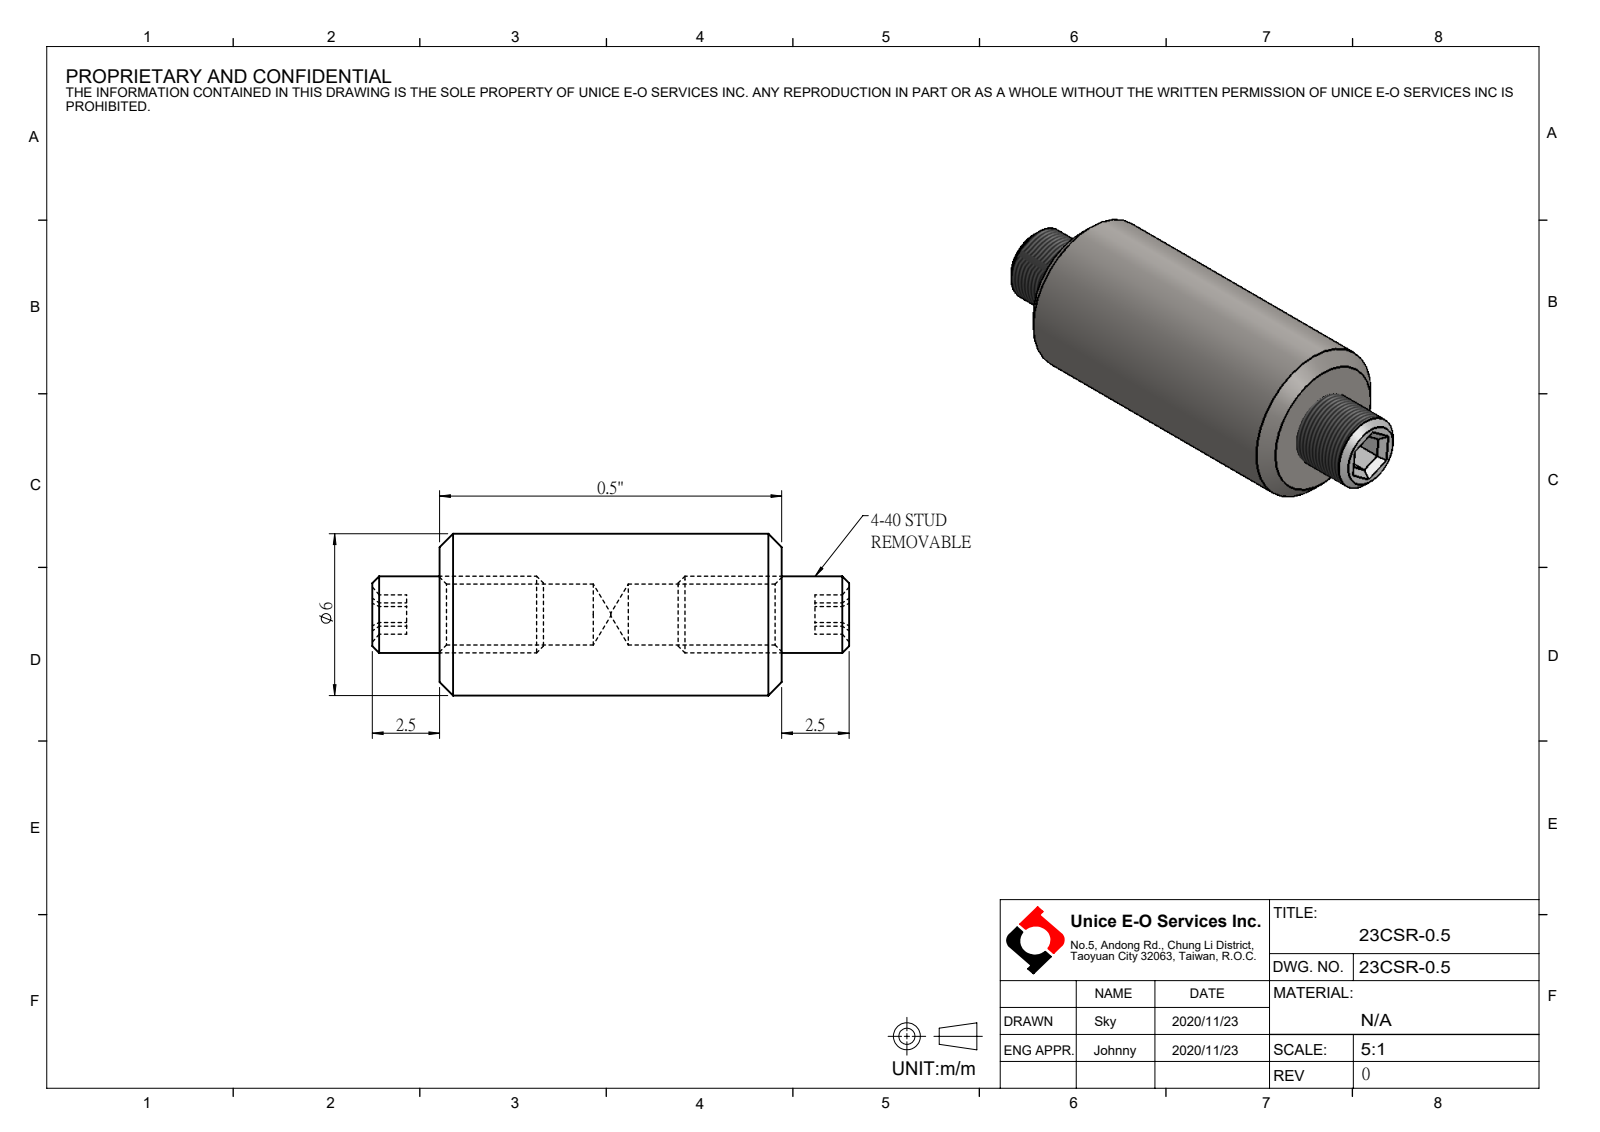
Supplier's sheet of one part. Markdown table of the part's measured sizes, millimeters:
| quantity | value |
| --- | --- |
| part name | 23CSR-0.5 |
| STEP written by | SolidWorks 2016 (AUTOMOTIVE_DESIGN) |
| units | millimeters |
| bodies | 0 solids, 42 faces (28 planar, 6 cylindrical, 8 other) |
| overall size | 17.7 × 6 × 6 |
| round bosses / shafts (diameter × count) | 6 × 1, 2.84 × 1 |
| main face-to-face distances | 12.7, 1.27, 2.5, 15.2, 17.7 |
